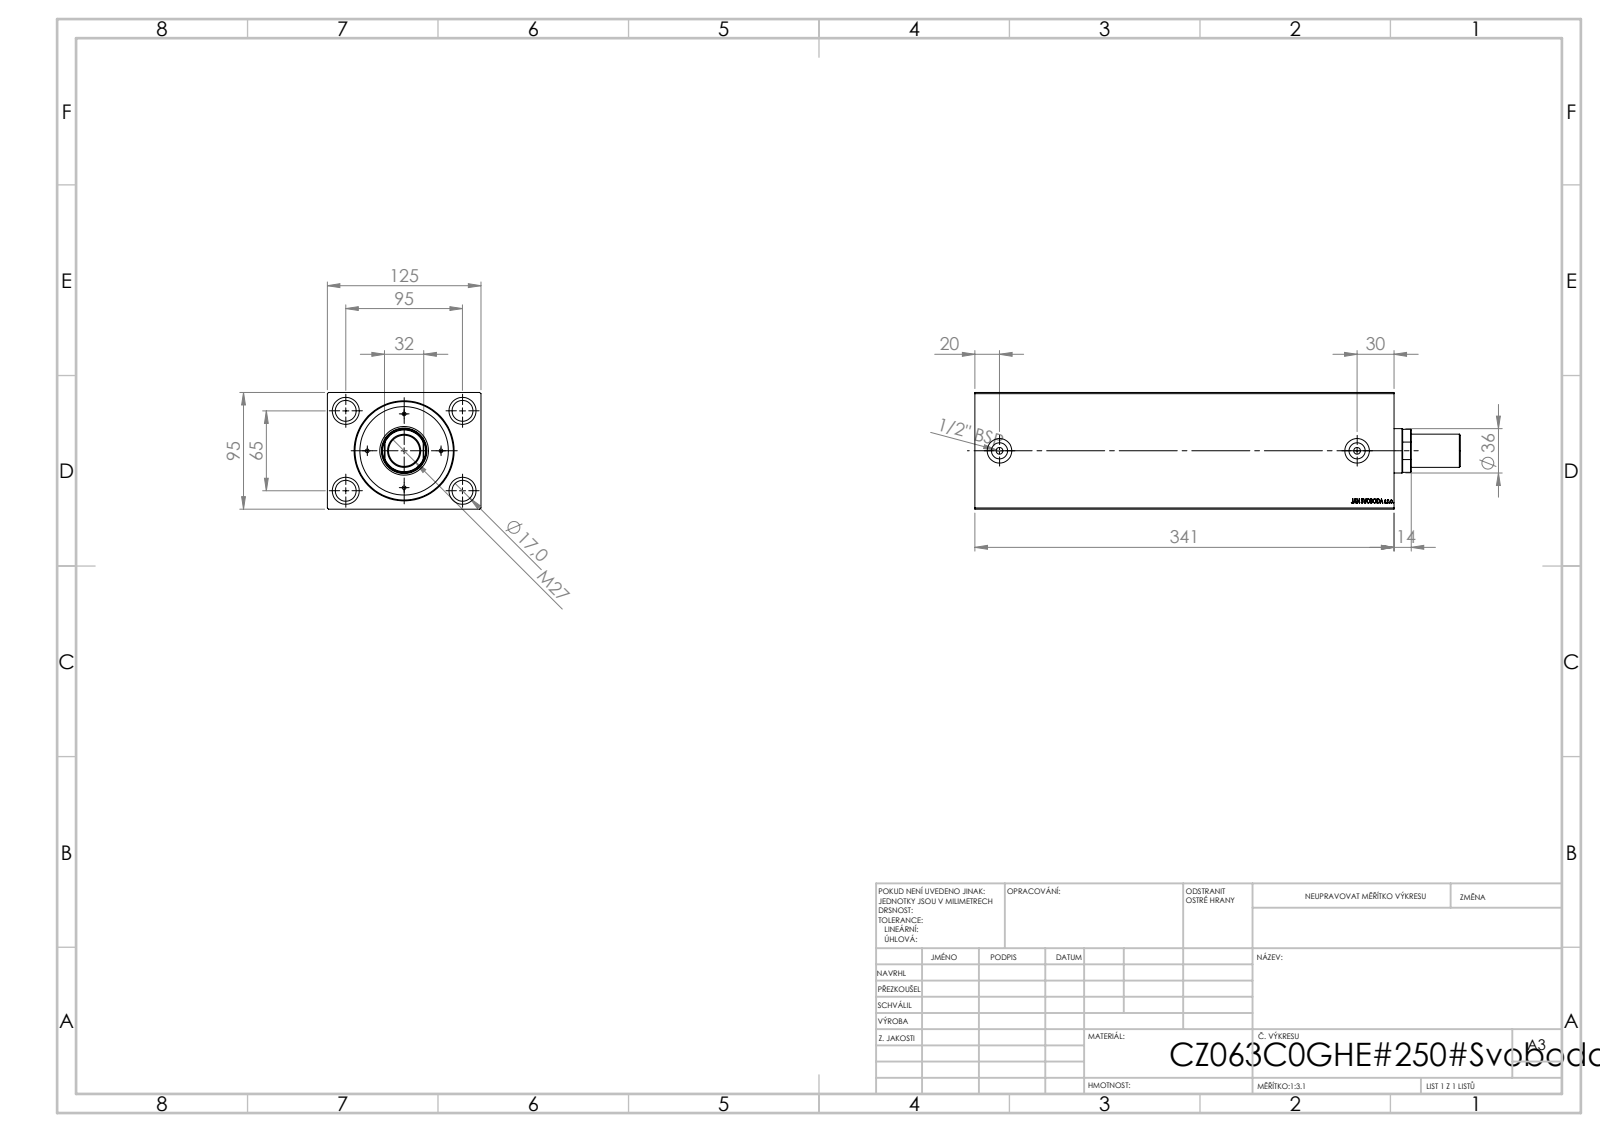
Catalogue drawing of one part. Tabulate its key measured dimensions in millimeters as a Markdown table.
| quantity | value |
| --- | --- |
| STEP written by | SolidWorks 2019 (CONFIG_CONTROL_DESIGN) |
| units | millimeters |
| bodies | 1 solid, 825 faces (397 planar, 46 cylindrical, 382 other) |
| overall size | 341 × 125 × 95 |
| volume | 2 697 000 mm³ |
| surface area | 310 930 mm² |
| round holes (diameter × count) | 17 × 4, 22 × 4, 5.5 × 2, 8 × 2, 13.16 × 2, 20 × 2, 36 × 1, 63 × 1, 80 × 1 |
| main face-to-face distances | 95, 125, 341, 320.2, 20.8, 14, 306.2, 327, 10.33, 330.67 |
| hole center spacings | 57.55, 65, 95, 115.11, 271, 291 |
